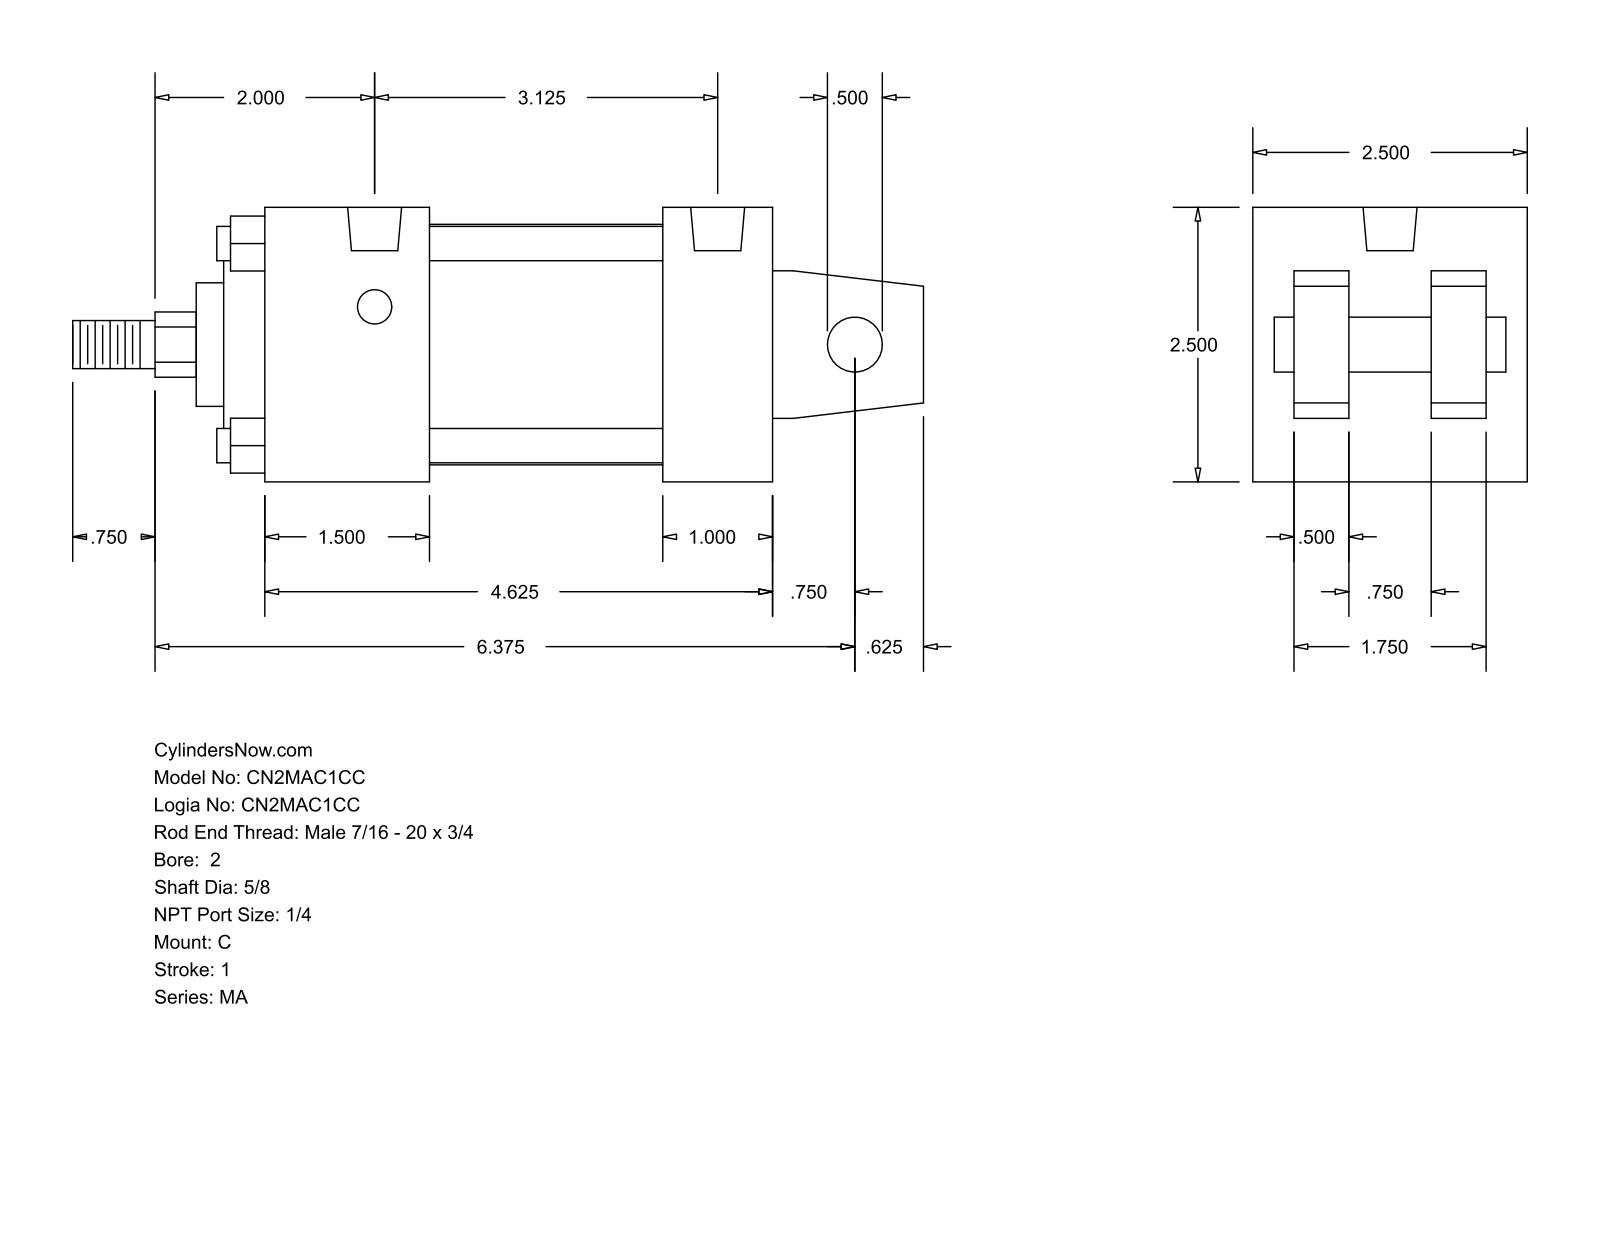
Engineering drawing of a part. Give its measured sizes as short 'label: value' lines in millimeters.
name: MA_C__0200_0.625
written by: GSSL Pune (CONFIG_CONTROL_DESIGN)
unit: mm
bodies: 0 solids, 105 faces (77 planar, 28 cylindrical, 0 other)
size: 196.85 × 63.5 × 63.5
holes: 4× ⌀7.94, 2× ⌀12.49
bosses: 4× ⌀7.94, 1× ⌀55.63, 1× ⌀50.8, 1× ⌀28.57, 1× ⌀15.88, 1× ⌀12.7, 1× ⌀11.11
rounds: 1× R7.54
face distances: 63.5, 9.52, 12.7, 22.22, 41.28, 53.98, 31.76, 53.97, 38.1, 117.48
hole spacings: 79.38
